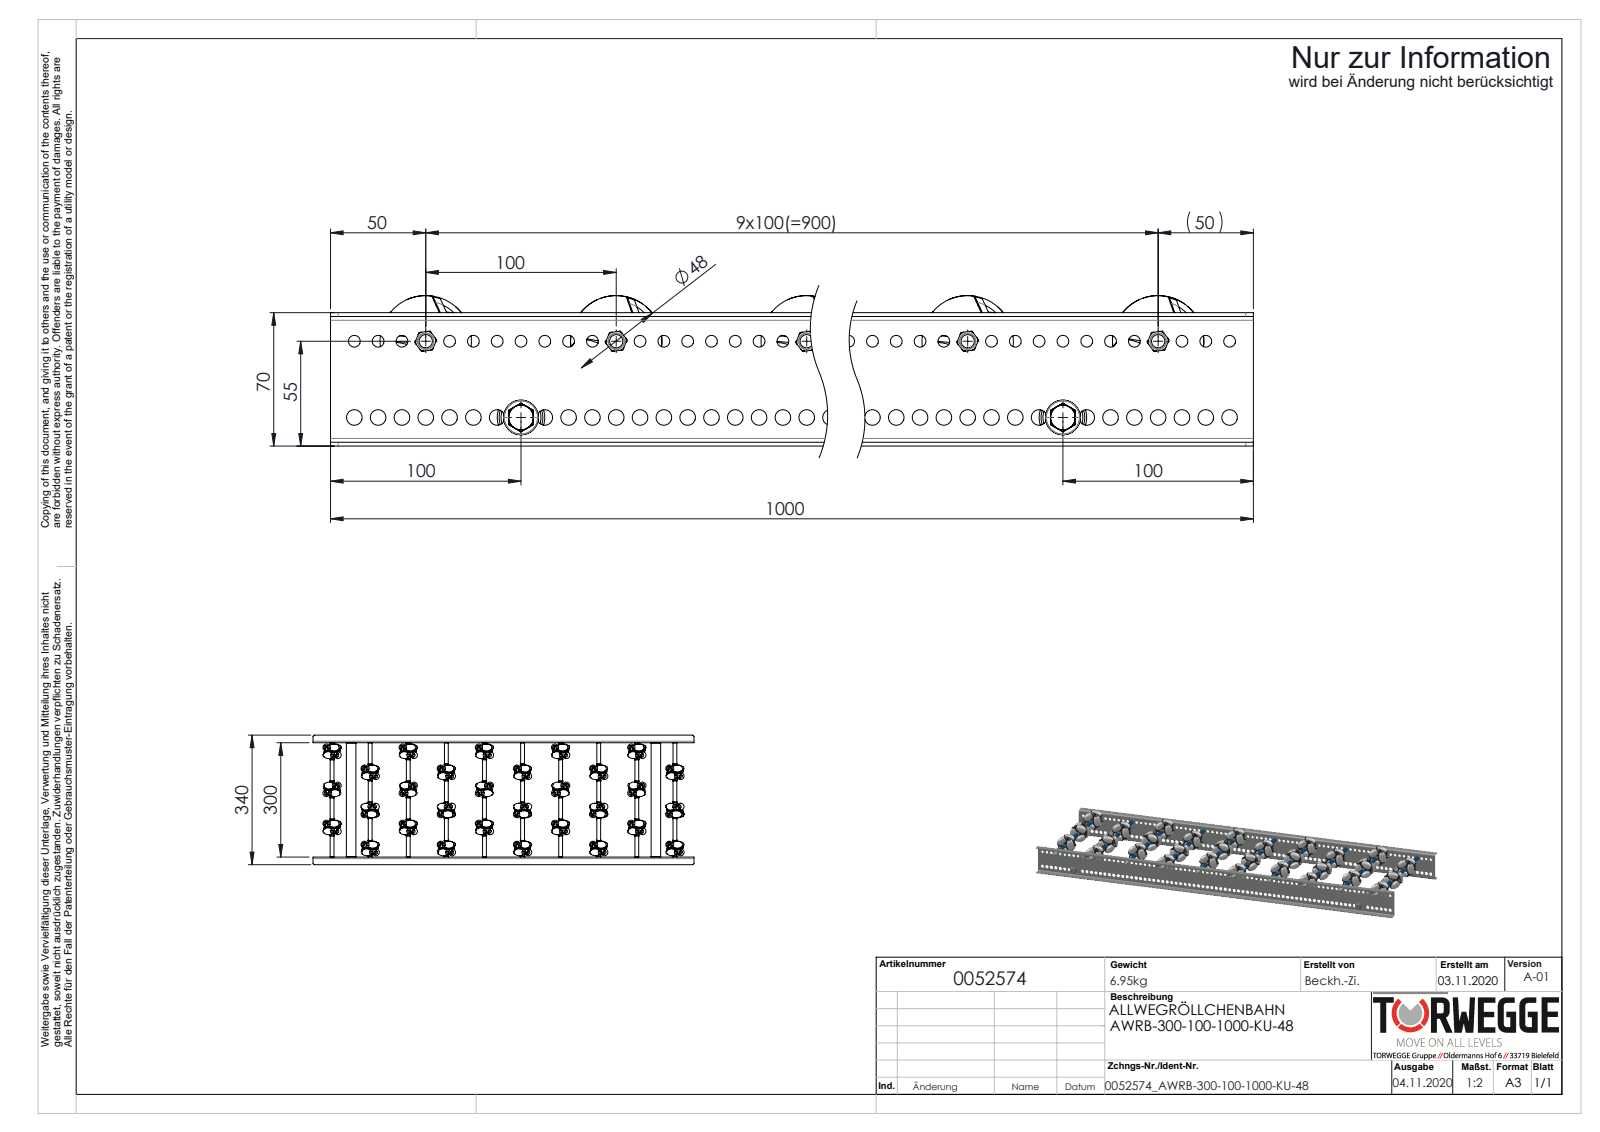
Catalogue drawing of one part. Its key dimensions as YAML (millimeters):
part_name: "Profil-RB-20x70x20x2_S100215_U-PROFIL-20-70-20-2-RB-L=1000; 0052574; AWR48_Halter; 0015028_AWR48 (+8 more)"
step_written_by: "SolidWorks 2020 (AUTOMOTIVE_DESIGN)"
units: millimeters
bodies: {solids: 522, faces: 9732, planar: 3240, cylindrical: 3908, other: 2584}
overall_size: [1000, 340, 78.99]
volume: 1950000
surface_area: 1423000
round_holes:
  - {diameter: 3.7, count: 180}
  - {diameter: 4.2, count: 180}
  - {diameter: 6.2, count: 79}
  - {diameter: 8.2, count: 79}
  - {diameter: 4.92, count: 10}
  - {diameter: 6.5, count: 10}
  - {diameter: 8.4, count: 10}
  - {diameter: 6.8, count: 2}
  - {diameter: 21, count: 2}
round_bosses_or_shafts:
  - {diameter: 4, count: 180}
  - {diameter: 3.7, count: 147}
  - {diameter: 8, count: 12}
  - {diameter: 42, count: 10}
  - {diameter: 11, count: 10}
  - {diameter: 10, count: 10}
  - {diameter: 7, count: 10}
  - {diameter: 6, count: 10}
partial_cylinders:
  - {radius: 23.55, count: 10}
  - {radius: 4, count: 8}
  - {radius: 2, count: 4}
face_to_face_distances: [2, 302, 68, 300, 304, 66, 70, 3, 20, 11.75]
hole_center_spacings: [36.06, 36.05, 100, 36.07, 36.04, 12.5, 200, 25]
